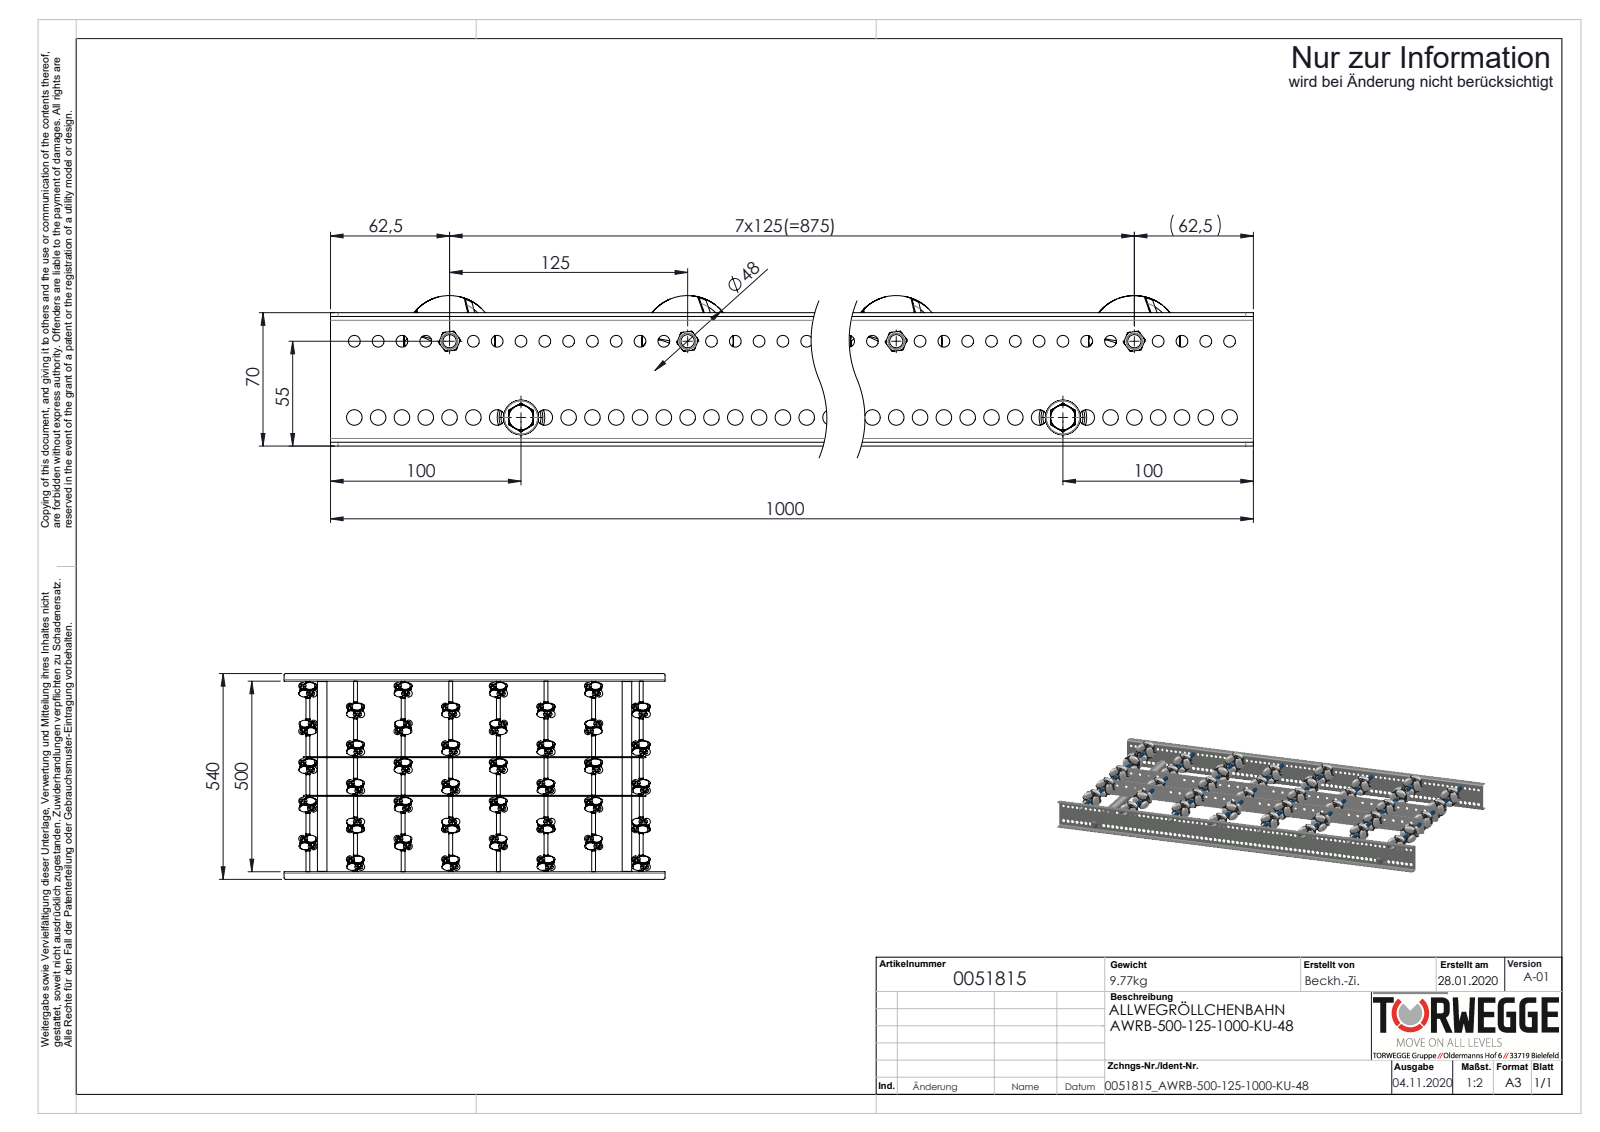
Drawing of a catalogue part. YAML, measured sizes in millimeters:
part_name: "Profil-RB-20x70x20x2_S100215_U-PROFIL-20-70-20-2-RB-L=1000; AWR48_Röllchen; Traversen_KFG_L500; 0027528_BUCHSE-HOHLNIETE ZU AWR48 (+8 more)"
step_written_by: "SolidWorks 2020 (AUTOMOTIVE_DESIGN)"
units: millimeters
bodies: {solids: 678, faces: 12484, planar: 4196, cylindrical: 5080, other: 3208}
overall_size: [1000, 540, 78.99]
volume: 2662000
surface_area: 1935000
round_holes:
  - {diameter: 3.7, count: 240}
  - {diameter: 4.2, count: 240}
  - {diameter: 6.2, count: 79}
  - {diameter: 8.2, count: 79}
  - {diameter: 6.5, count: 36}
  - {diameter: 4.92, count: 8}
  - {diameter: 8.4, count: 8}
  - {diameter: 6.8, count: 2}
  - {diameter: 21, count: 2}
round_bosses_or_shafts:
  - {diameter: 4, count: 240}
  - {diameter: 3.7, count: 207}
  - {diameter: 8, count: 10}
  - {diameter: 42, count: 8}
  - {diameter: 11, count: 8}
  - {diameter: 10, count: 8}
  - {diameter: 7, count: 8}
  - {diameter: 6, count: 8}
partial_cylinders:
  - {radius: 4, count: 8}
  - {radius: 23.55, count: 8}
  - {radius: 2, count: 4}
  - {radius: 5, count: 4}
face_to_face_distances: [2, 502, 101.5, 2.5, 68, 500, 504, 99, 200.1, 301.6]
hole_center_spacings: [36.06, 36.05, 36.07, 125, 250, 36.04, 12.5, 25]
